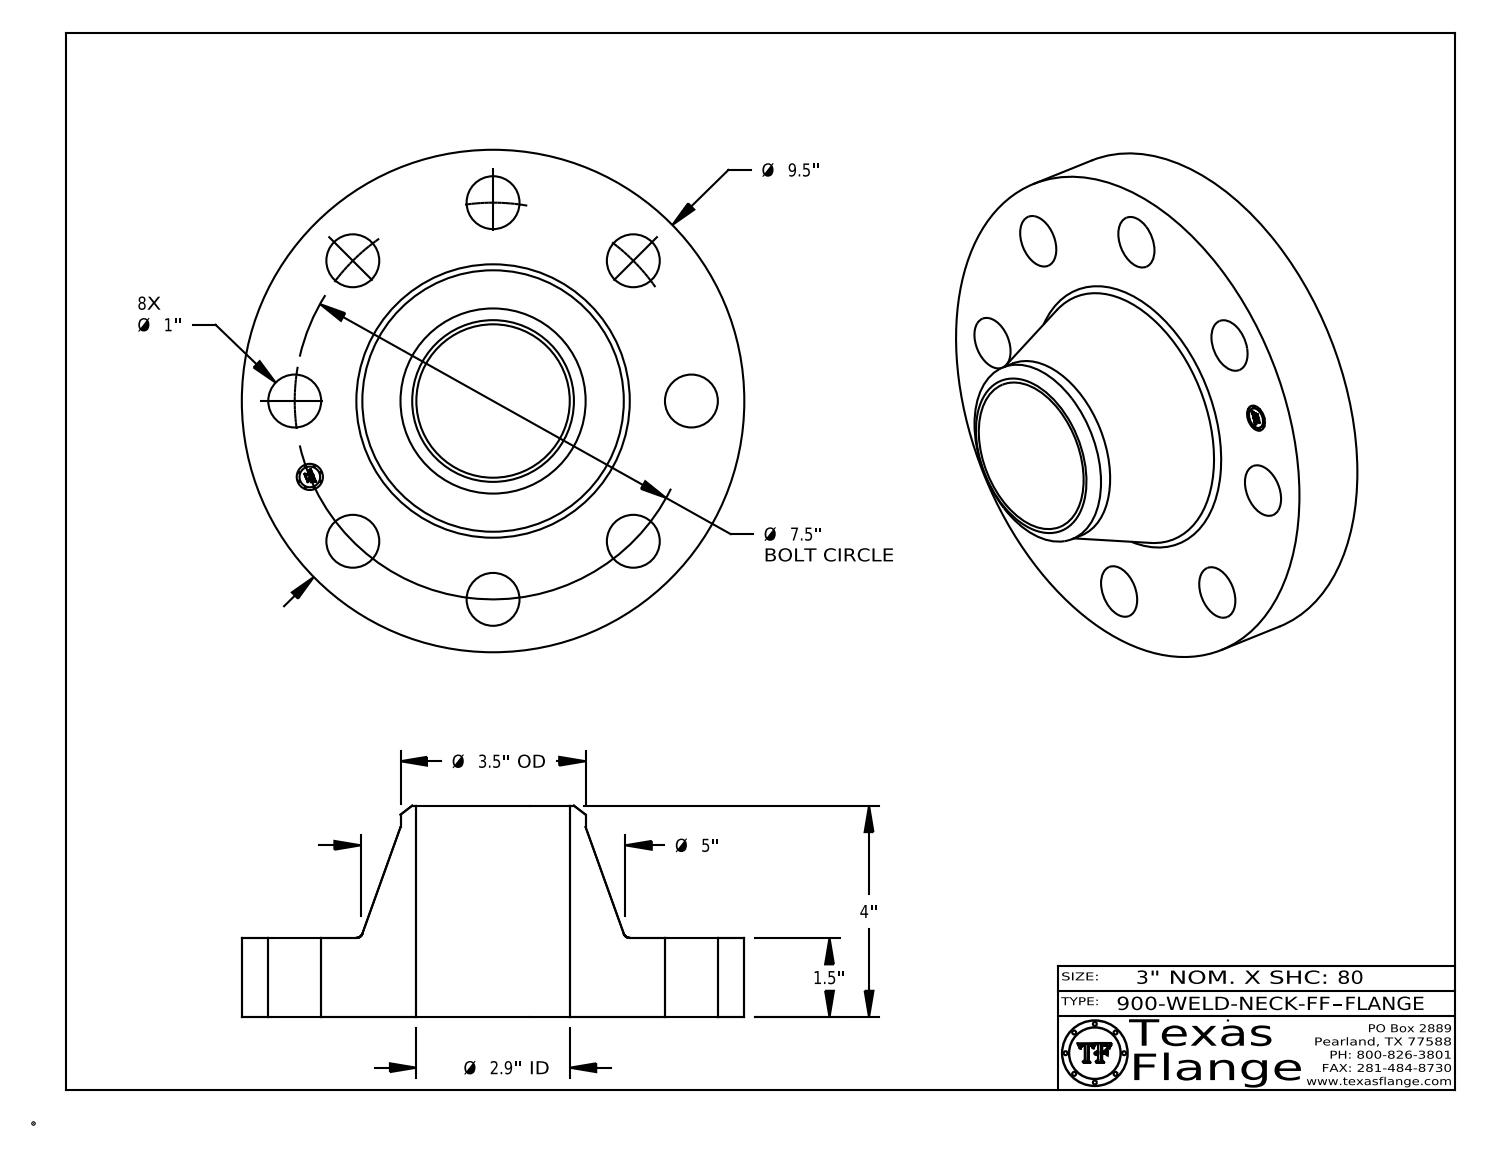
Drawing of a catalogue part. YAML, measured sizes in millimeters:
part_name: "900-WELD-NECK-FF"
step_written_by: "CATIA V5 STEP AP214 (AUTOMOTIVE_DESIGN)"
units: millimeters
bodies: {solids: 1, faces: 416, planar: 368, cylindrical: 42, other: 6}
overall_size: [241.3, 241.3, 101.6]
volume: 1708000
surface_area: 166100
round_holes:
  - {diameter: 25.4, count: 8}
  - {diameter: 12.6, count: 1}
  - {diameter: 73.7, count: 1}
round_bosses_or_shafts:
  - {diameter: 0.8, count: 8}
  - {diameter: 241.3, count: 1}
  - {diameter: 88.9, count: 1}
  - {diameter: 9.9, count: 1}
face_to_face_distances: [38.1, 101.6, 63.5, 0.4, 37.7, 63.9, 3.8, 3.7, 0.7, 2.4]
hole_center_spacings: [95.3, 72.9, 134.7, 176, 37.2, 158.4, 186.8, 190.5]
